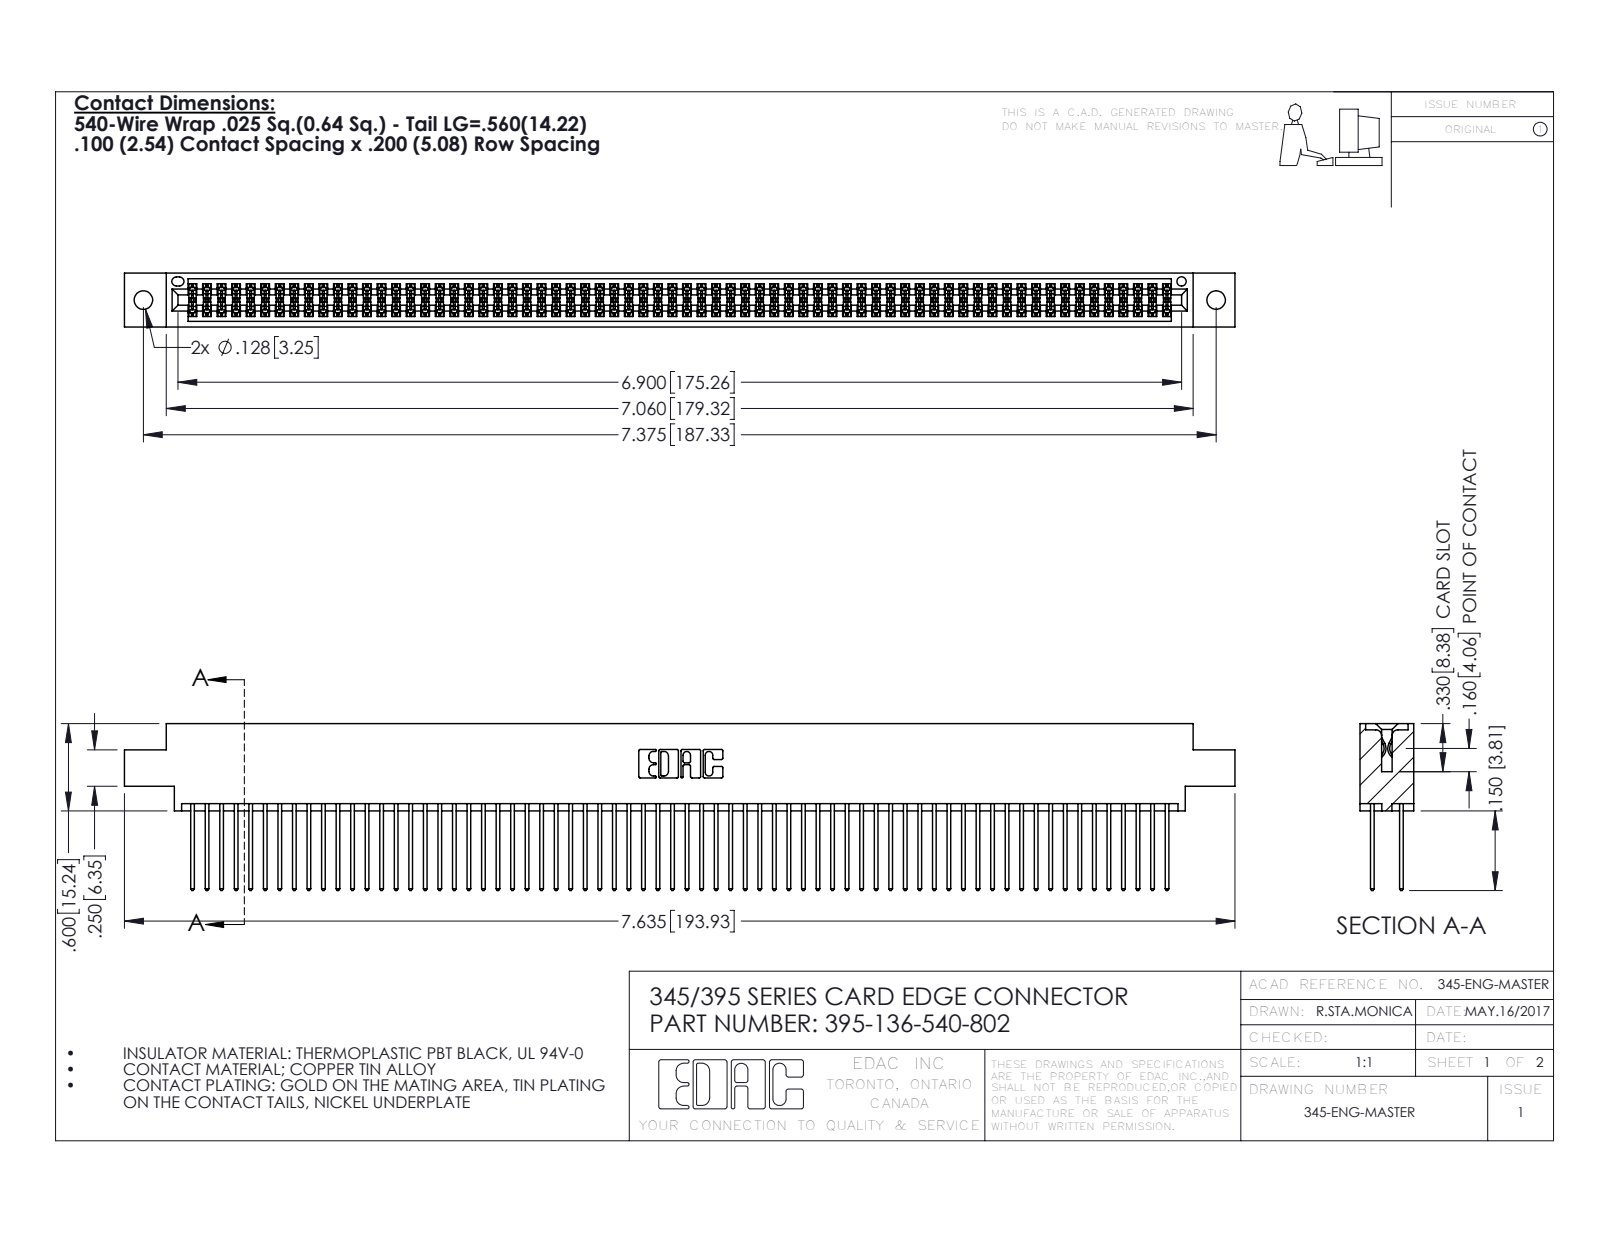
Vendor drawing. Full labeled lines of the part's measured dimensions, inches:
Part name (STEP PRODUCT): 395-136-540-802; 345 Part_0.170 Offset - 0.128 Dia; 345-292-001_345-293-140
STEP written by: SolidWorks 2016 (CONFIG_CONTROL_DESIGN)
Units: inches
Bodies: 137 solids, 6930 faces (4572 planar, 2358 cylindrical, 0 other)
Overall size (bounding box): 7.635 × 1.147 × 0.37
Volume: 1.187 in³ · Surface area: 48.84 in²
Round holes (diameter × count): ⌀0.128 ×2, ⌀0.064 ×1
Partial cylindrical surfaces — rounded edges, fillets, slot ends (radius × count): R0.006 ×204, R0.01 ×136, R0.01 ×22, R0.007 ×6, R0.031 ×6, R0.026 ×3, R0.014 ×2, R0.019 ×2
Main face-to-face distances: 0.072, 0.298, 0.2, 0.098, 0.272, 0.025, 0.37, 0.225, 0.175, 0.149
Hole centre spacings: 0.27, 7.139, 7.375
